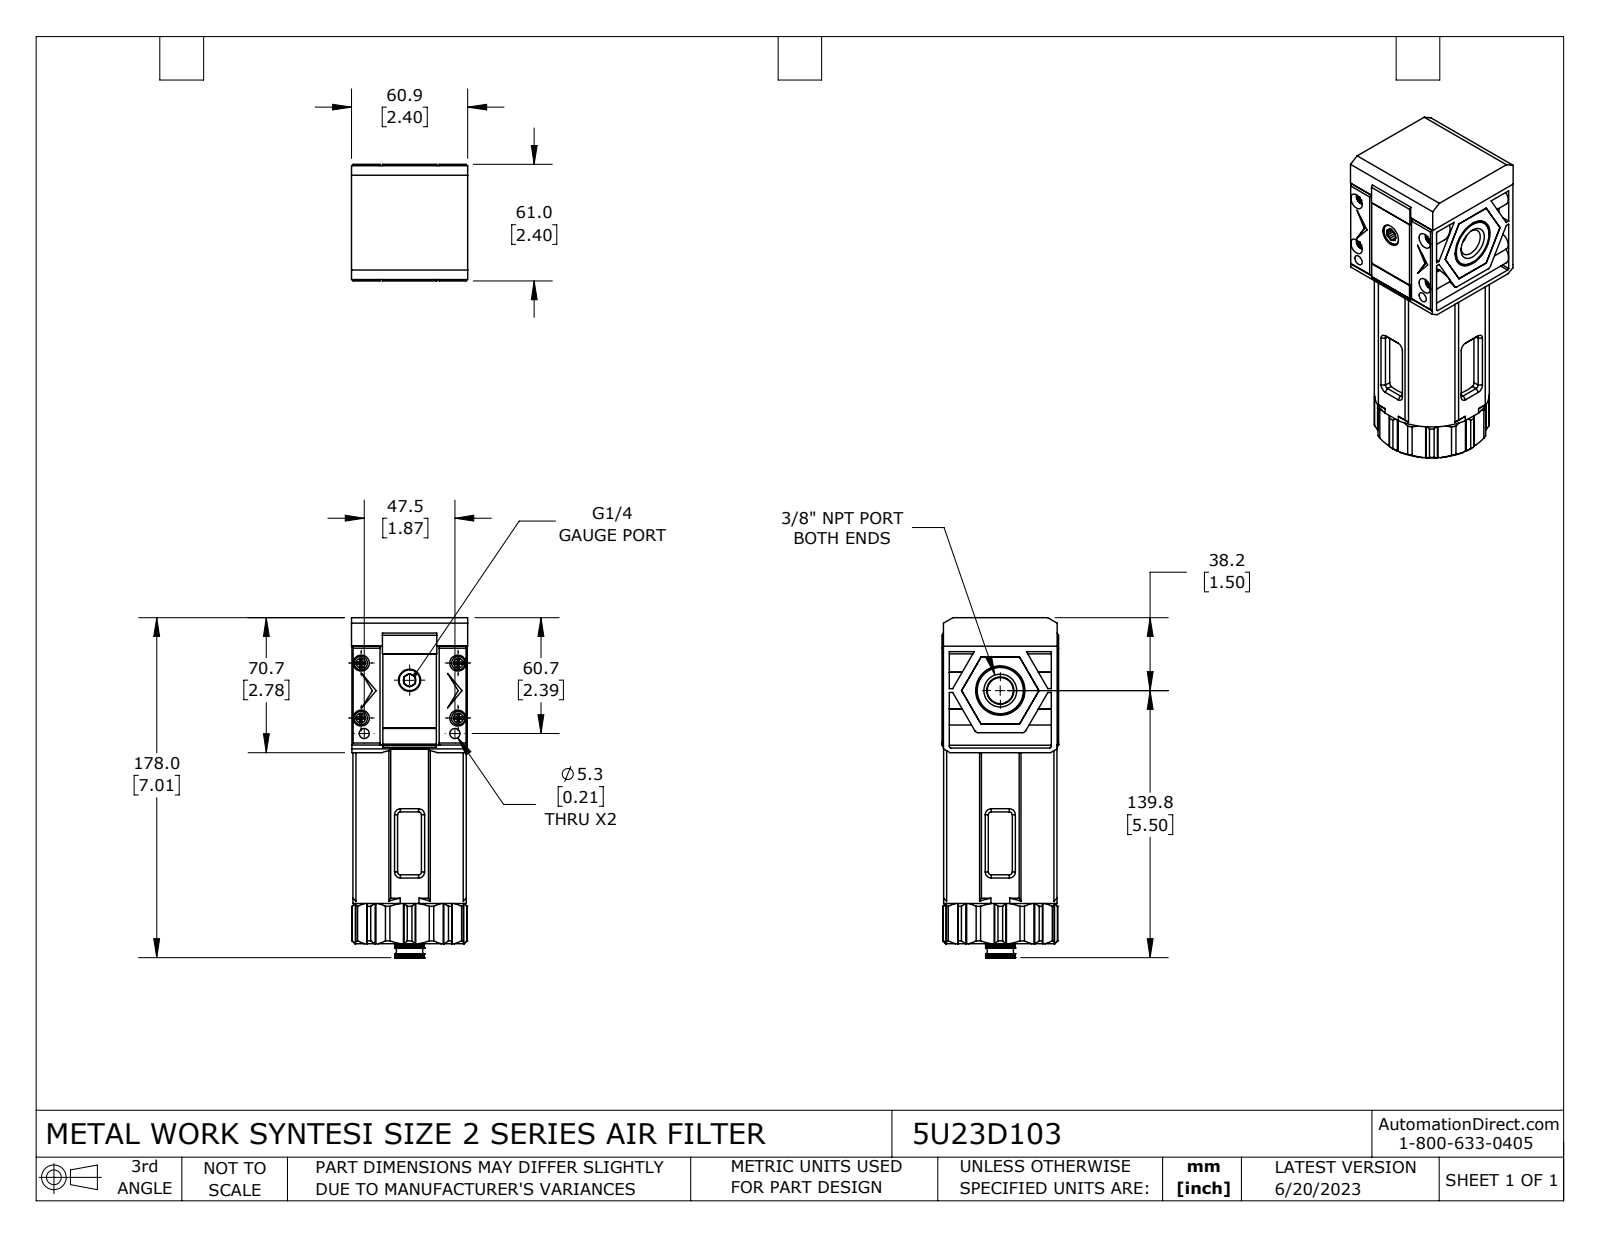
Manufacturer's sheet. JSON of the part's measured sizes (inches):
{"part_name": "5U23D103", "step_written_by": "SolidWorks 2021 (CONFIG_CONTROL_DESIGN)", "units": "inches", "bodies": {"solids": 14, "faces": 1420, "planar": 963, "cylindrical": 255, "other": 202}, "overall_size": [7.008, 2.402, 2.398], "volume_in3": 23.99, "surface_area_in2": 187.9, "round_holes": [[0.128, 4], [0.165, 4], [0.331, 4], [0.209, 2], [0.126, 1], [0.276, 1], [0.343, 1], [0.457, 1], [1.26, 1], [1.929, 1], [1.969, 1], [2.008, 1]], "round_bosses_or_shafts": [[0.276, 4], [0.189, 4], [0.15, 4], [1.248, 1], [1.035, 1], [0.925, 1], [0.917, 1], [0.638, 1]], "partial_cylinders_radius": [[0.02, 16], [0.059, 8], [0.191, 4], [0.008, 2], [0.079, 2], [0.242, 2], [0.12, 1], [0.276, 1]], "face_to_face_distances": [2.39, 5.303, 3.205, 2.098, 0.591, 2.689, 1.13, 5.894, 2.193, 2.402], "hole_center_spacings": [0.325, 1.057, 1.134, 1.265, 1.443, 1.454, 1.957, 1.992]}
